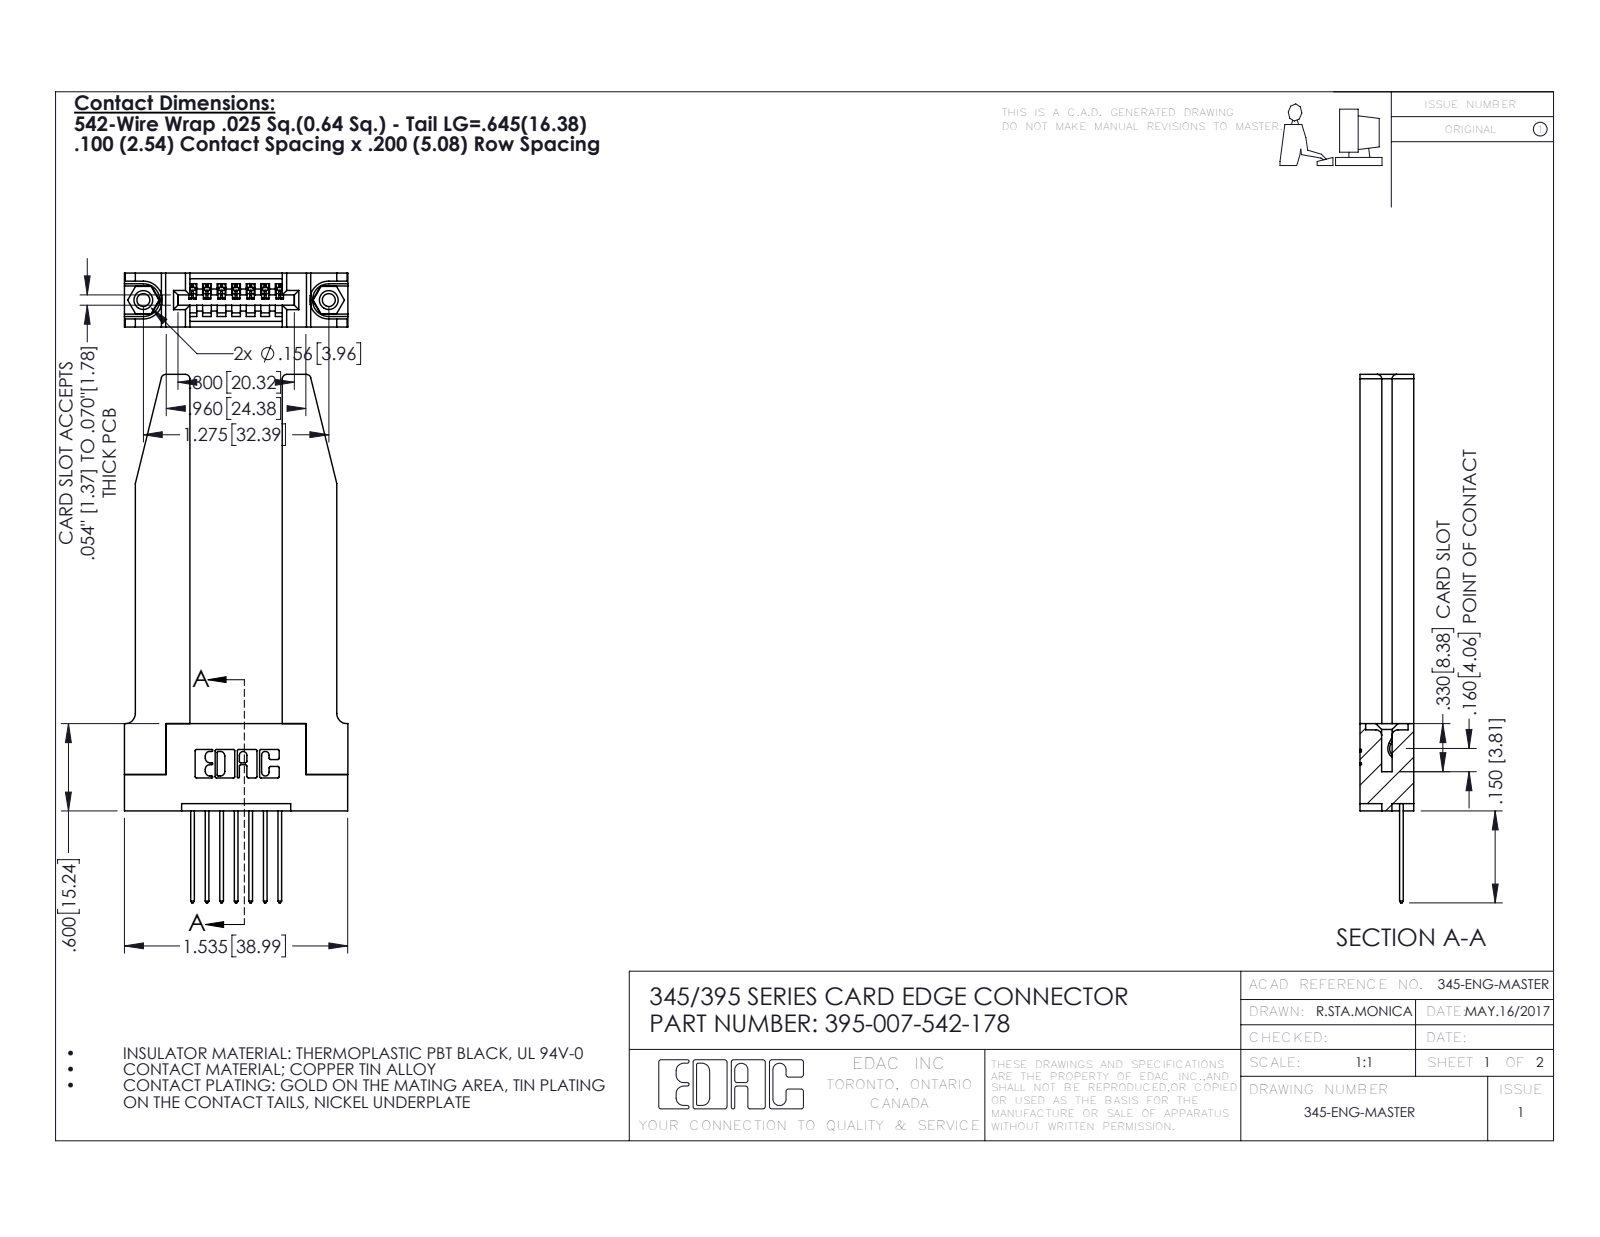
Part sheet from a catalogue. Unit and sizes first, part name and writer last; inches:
Units: inches
Overall size (bounding box): 3.632 × 1.536 × 0.37
Round holes (diameter × count): ⌀0.089 ×2, ⌀0.125 ×2, ⌀0.156 ×2, ⌀0.064 ×1
Round bosses / shafts (diameter × count): ⌀0.155 ×2
Partial cylindrical surfaces — rounded edges, fillets, slot ends (radius × count): R0.01 ×22, R0.006 ×14, R0.01 ×14, R0.03 ×8, R0.007 ×6, R0.031 ×6, R0.026 ×3, R0.031 ×2
Main face-to-face distances: 0.37, 0.15, 0.072, 0.22, 0.298, 0.148, 0.635, 0.077, 0.2, 0.095
Hole centre spacings: 0.27, 1.045, 1.275
Volume: 0.684 in³ · Surface area: 17.1 in²
Bodies: 12 solids, 766 faces (502 planar, 212 cylindrical, 52 other)
Part name (STEP PRODUCT): 345-292-001_345-293-142; 345 Part_Flush Mounting Lugs - 0.156 Dia-TH; 395-007-542-178; 345-220-078_345-220-078 (+1 more)
STEP written by: SolidWorks 2016 (CONFIG_CONTROL_DESIGN)
